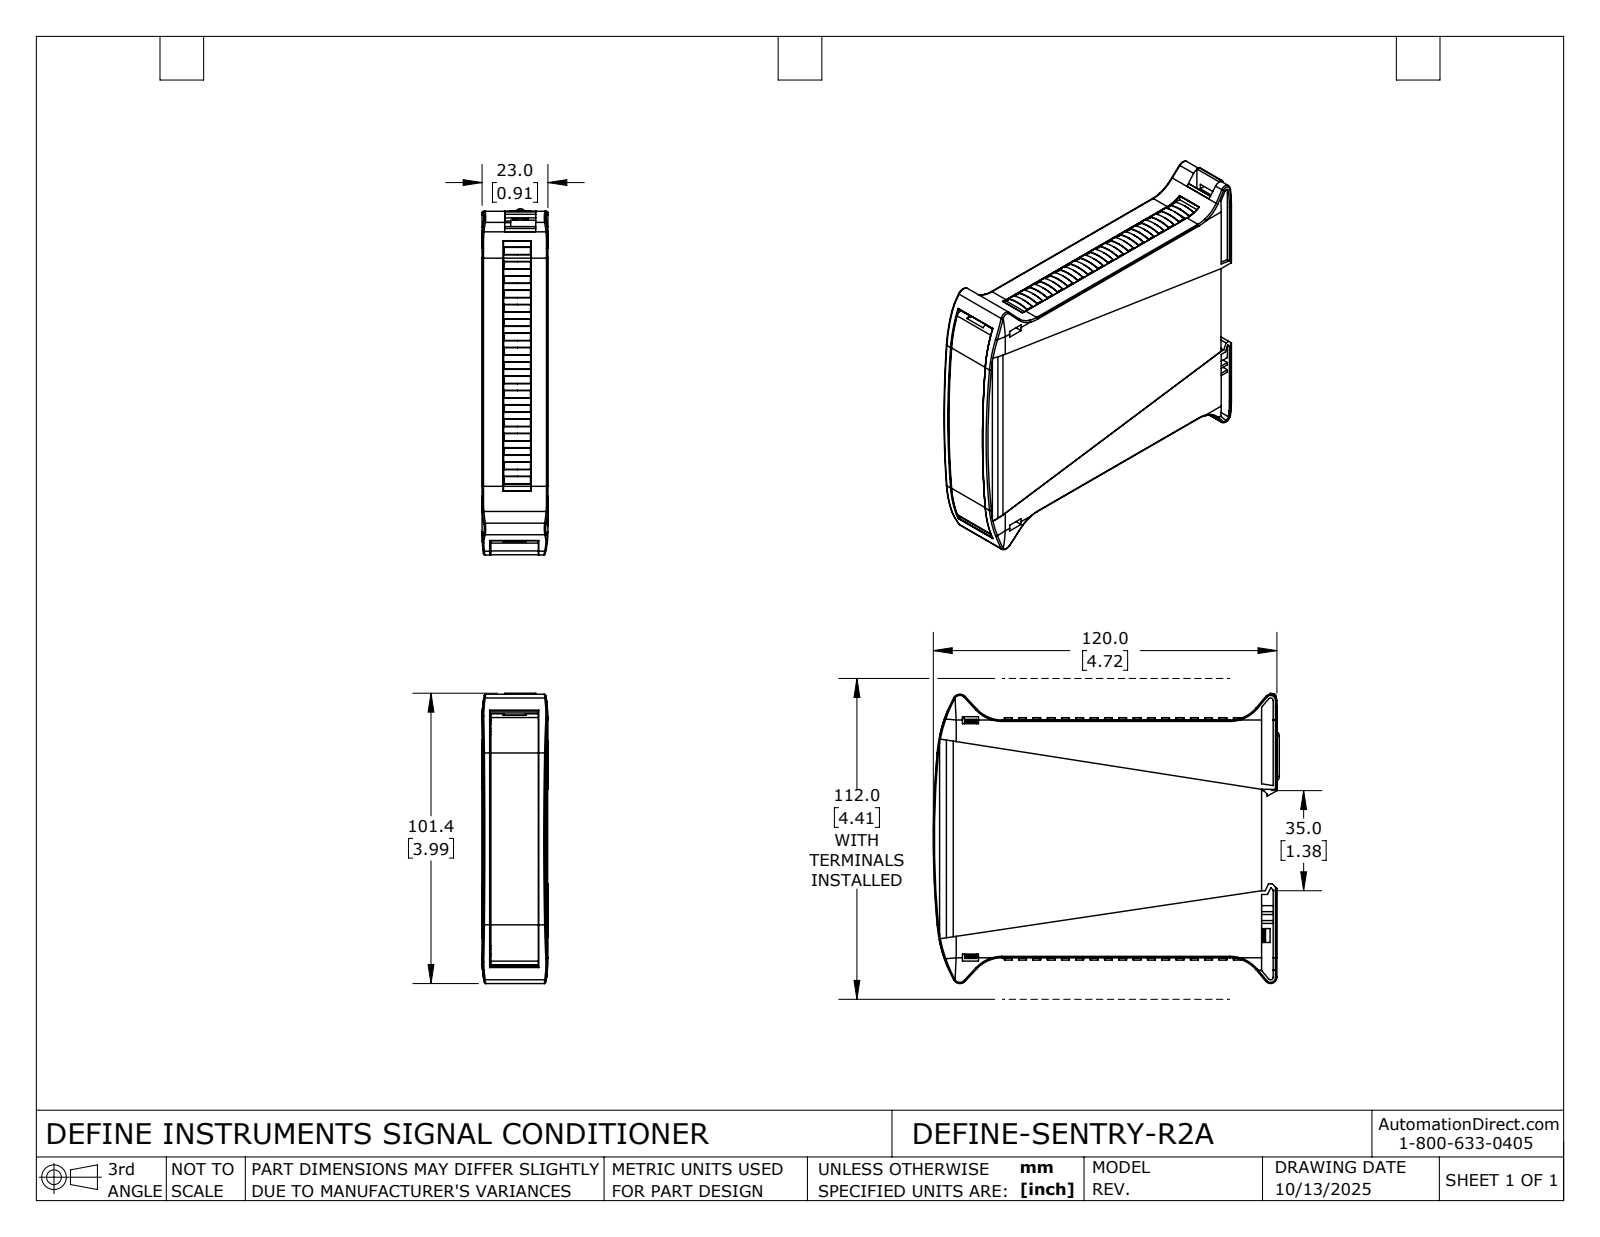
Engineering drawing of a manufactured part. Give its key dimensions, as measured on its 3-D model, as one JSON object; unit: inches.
{"part_name": "DEFINE-SENTRY-R2A", "step_written_by": "SolidWorks 2024 (AUTOMOTIVE_DESIGN)", "units": "inches", "bodies": {"solids": 8, "faces": 1941, "planar": 1188, "cylindrical": 523, "other": 230}, "overall_size": [5.528, 4.757, 3.785], "volume_in3": 4.585, "surface_area_in2": 109.4, "round_holes": [[0.118, 4], [0.075, 1], [0.146, 1], [0.241, 1]], "round_bosses_or_shafts": [[0.089, 1]], "partial_cylinders_radius": [[0.01, 15], [0.02, 11], [0.006, 10], [0.004, 4], [0.039, 4], [0.472, 4], [1.893, 4], [0.079, 3]], "face_to_face_distances": [0.675, 0.055, 0.902, 0.167, 0.73, 0.843, 0.898, 0.734, 0.171, 0.059], "hole_center_spacings": [4.058, 5.368, 0.268, 0.739, 3.268, 3.546, 3.78, 4.175]}
